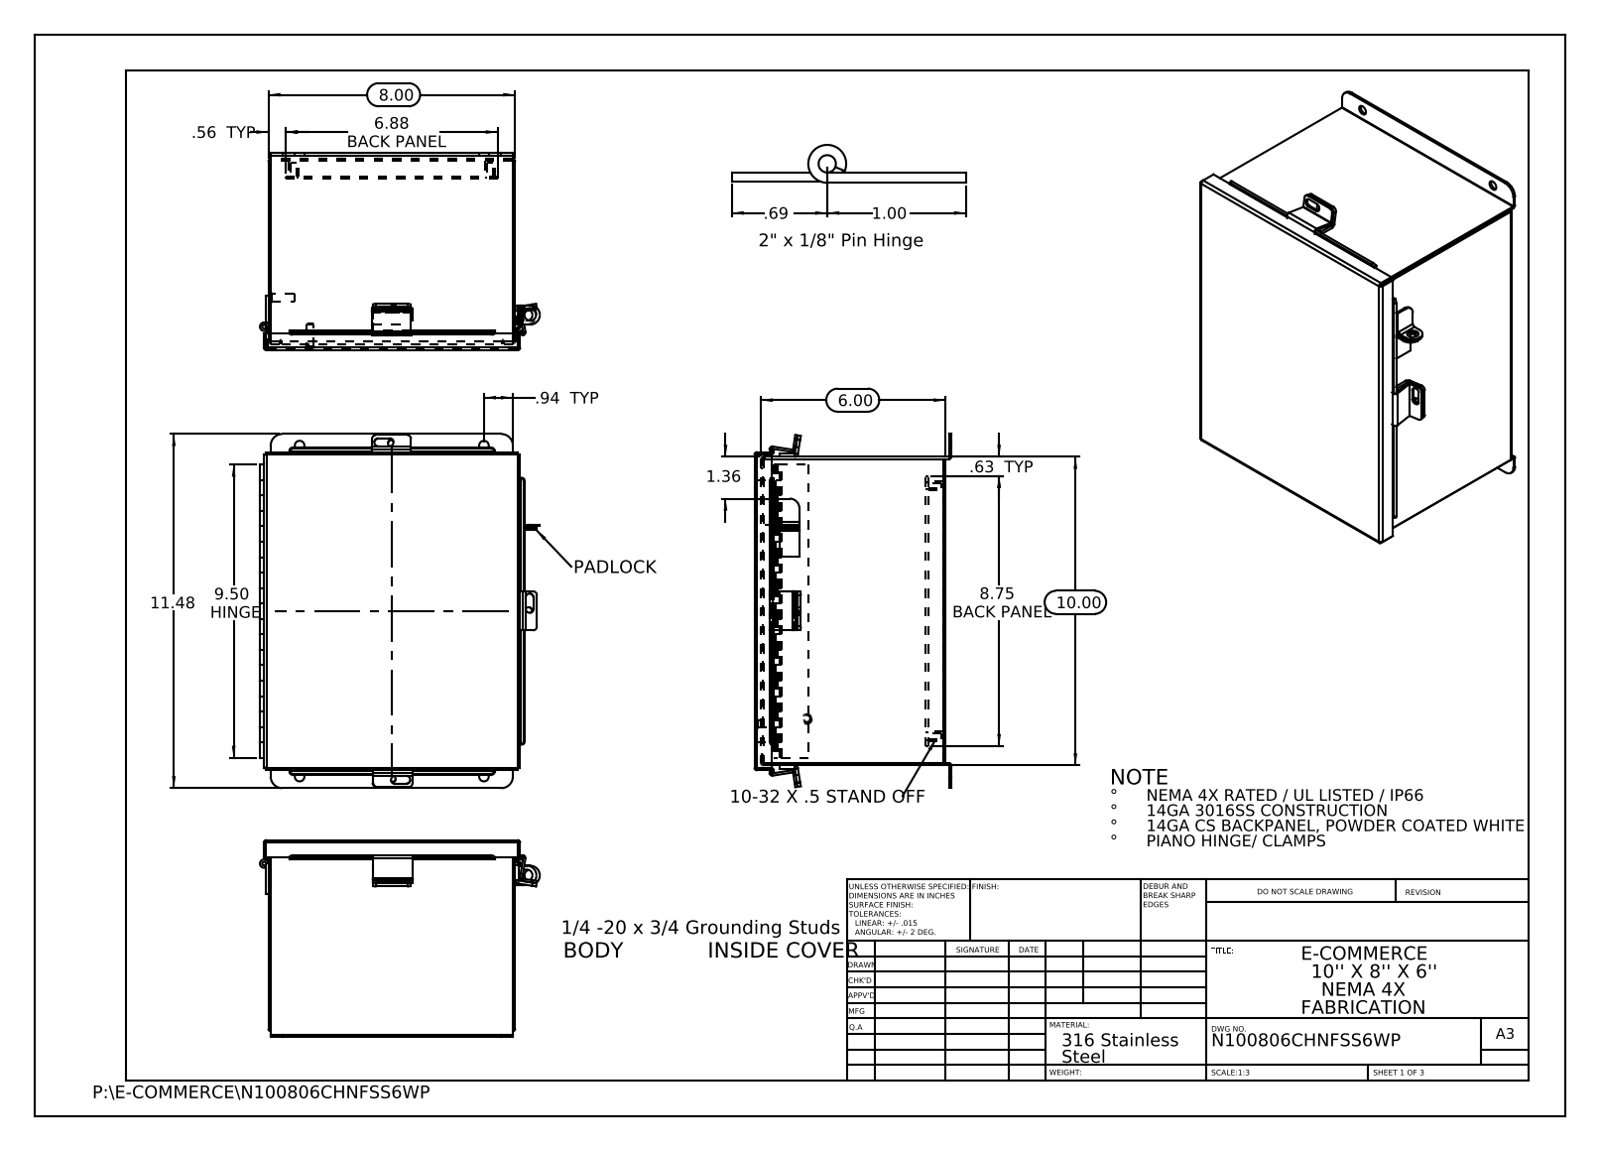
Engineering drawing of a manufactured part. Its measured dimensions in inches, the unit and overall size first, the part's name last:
Units: inches
Overall size (bounding box): 11.476 × 9.072 × 6.39
Round holes (diameter × count): ⌀0.25 ×7, ⌀0.187 ×4, ⌀0.312 ×4, ⌀0.125 ×1, ⌀0.373 ×1, ⌀0.375 ×1
Round bosses / shafts (diameter × count): ⌀0.313 ×4, ⌀0.315 ×2, ⌀0.236 ×2, ⌀0.273 ×1, ⌀0.25 ×1
Partial cylindrical surfaces — rounded edges, fillets, slot ends (radius × count): R0.013 ×13, R0.009 ×12, R0.088 ×12, R0.125 ×10, R0.083 ×6, R0.1 ×6, R0.133 ×6, R0.375 ×4
Main face-to-face distances: 0.075, 6.128, 7.925, 9.925, 6.053, 6.203, 0.074, 0.575, 0.5, 5.553
Hole centre spacings: 1.315, 6.311, 9.428, 11.269, 5.976, 6.375, 8.126, 10.328
Volume: 38.22 in³ · Surface area: 1 047 in²
Bodies: 21 solids, 620 faces (383 planar, 217 cylindrical, 20 other)
Part name (STEP PRODUCT): N100806CHNFSS6WP Hinge Cover Side JIC; N100806CHNFSS6WP Hinge Body Side; N100806CHNFSS6WP JIC Cover Clamp; N100806CHNFSS6WP JIC Clamp Bracket (+8 more)
STEP written by: SolidWorks 2013 (CONFIG_CONTROL_DESIGN)
